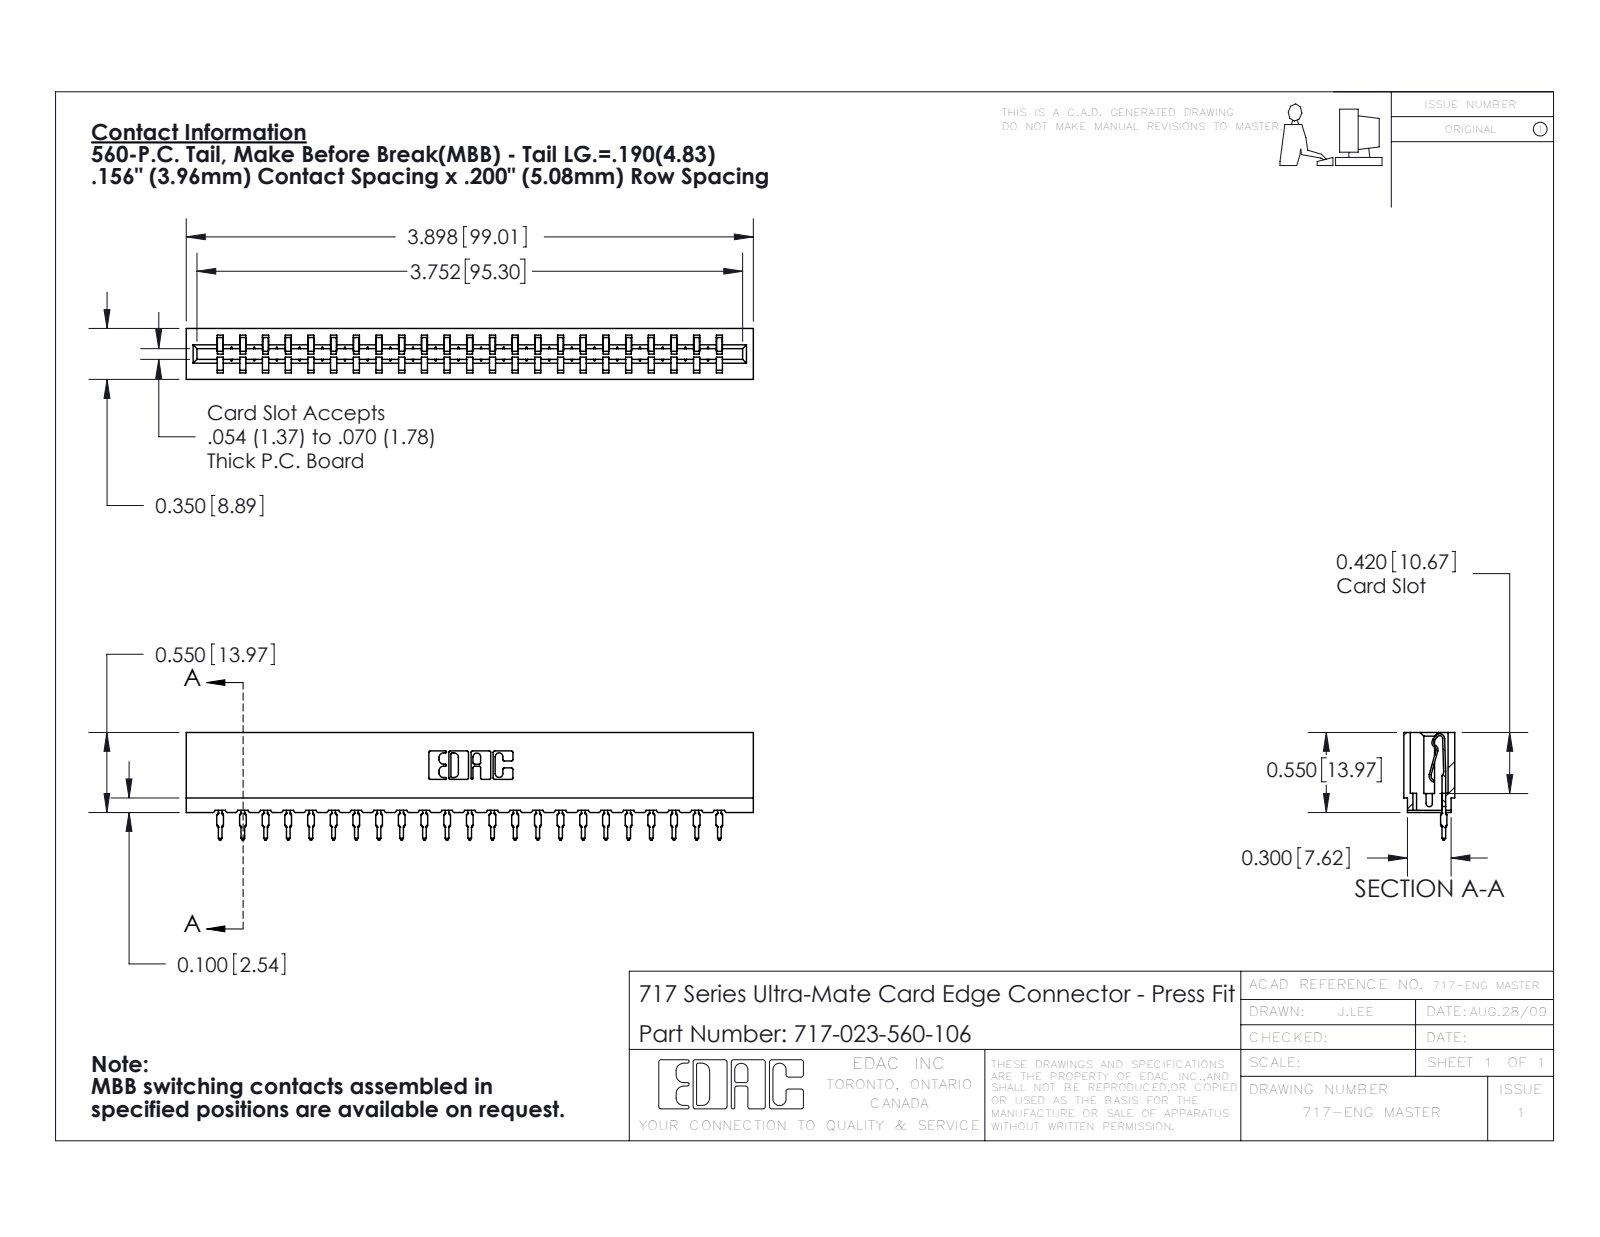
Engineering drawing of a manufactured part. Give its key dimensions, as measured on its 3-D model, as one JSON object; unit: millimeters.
{"part_name": "717 Part_Insulator Option - 06; 745-292-001_560; 717-023-560-106", "step_written_by": "SolidWorks 2016 (CONFIG_CONTROL_DESIGN)", "units": "millimeters", "bodies": {"solids": 24, "faces": 2900, "planar": 1733, "cylindrical": 569, "other": 598}, "overall_size": [99, 18.8, 8.9], "volume_mm3": 8520, "surface_area_mm2": 12130, "partial_cylinders_radius": [[0.4, 46], [0.5, 46], [0.3, 22], [0.2, 6], [0.8, 6], [0.1, 4], [0.3, 4], [0.7, 3]], "face_to_face_distances": [5.4, 3.5, 8.9, 4, 1.9, 15.8, 1.1, 0.6, 7.7, 2.4]}
